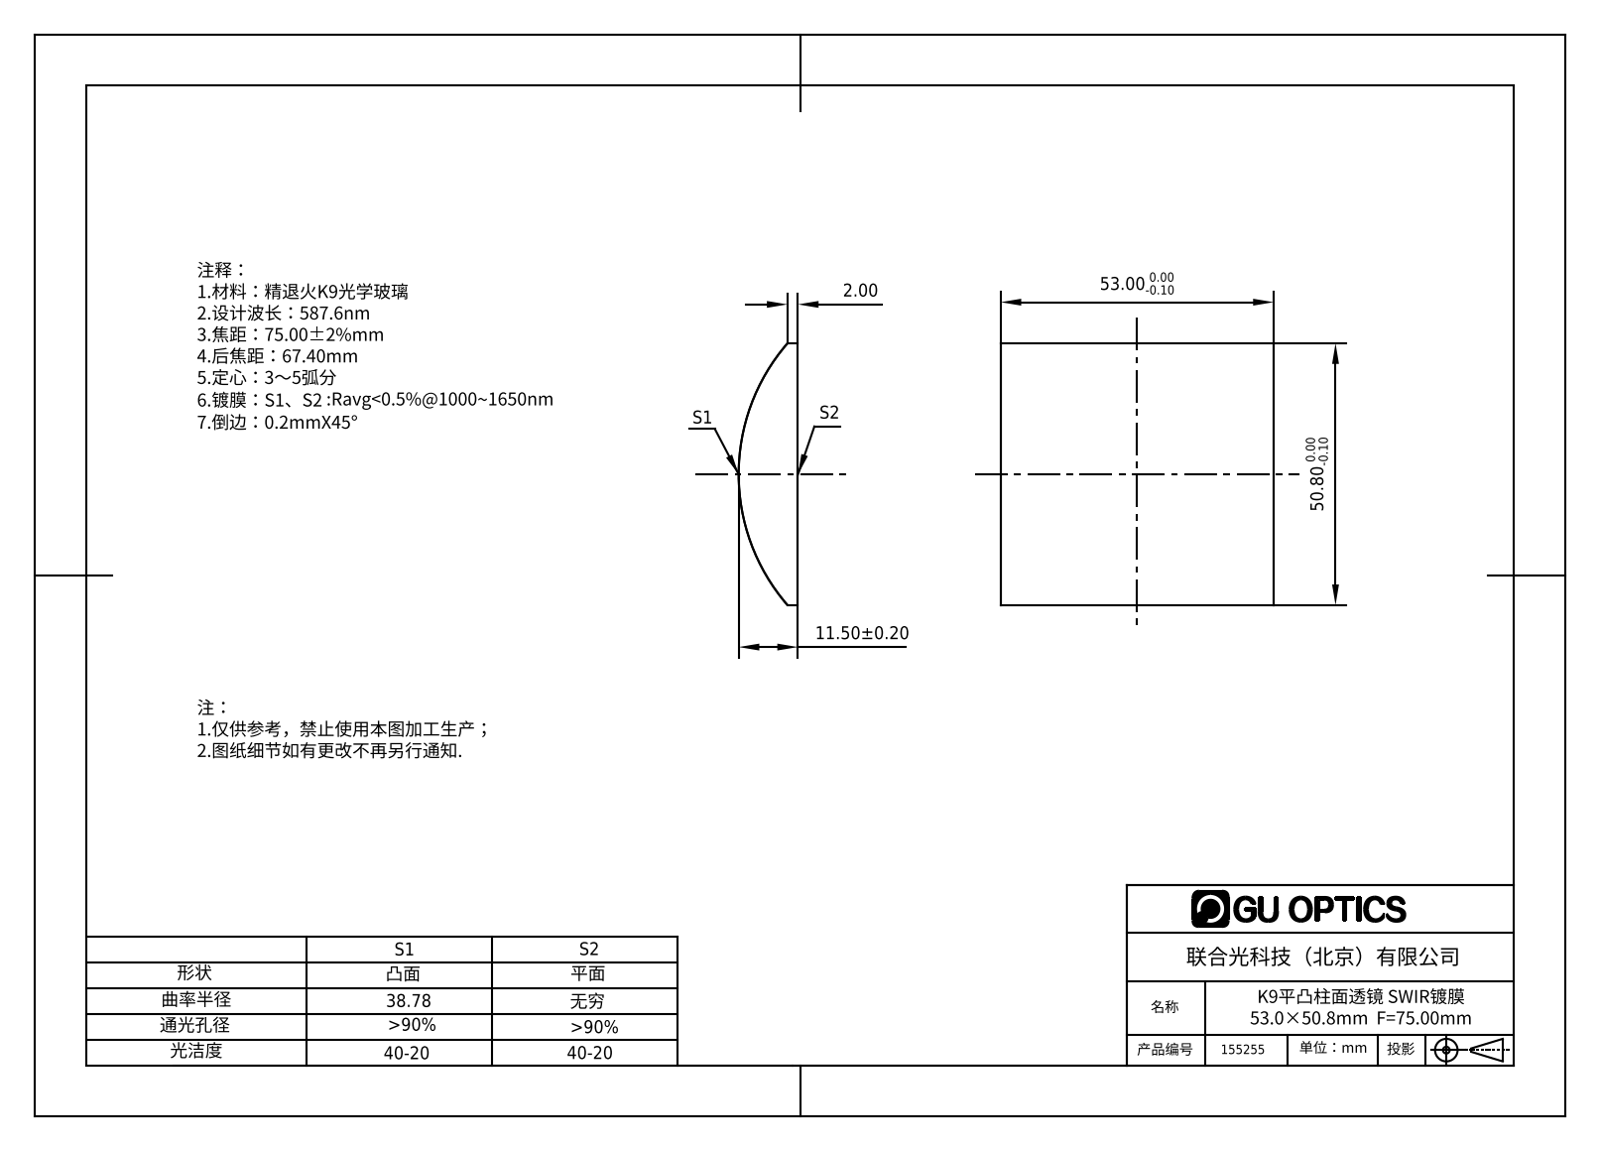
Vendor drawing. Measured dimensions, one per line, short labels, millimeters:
name: 155057
written by: SolidWorks 2016 (AUTOMOTIVE_DESIGN)
unit: mm
bodies: 1 solid, 6 faces (5 planar, 1 cylindrical, 0 other)
size: 53 × 50.8 × 11.5
volume: 22 923 mm³; area: 6 708 mm²
rounds: 1× R38.78
face distances: 53, 50.8
